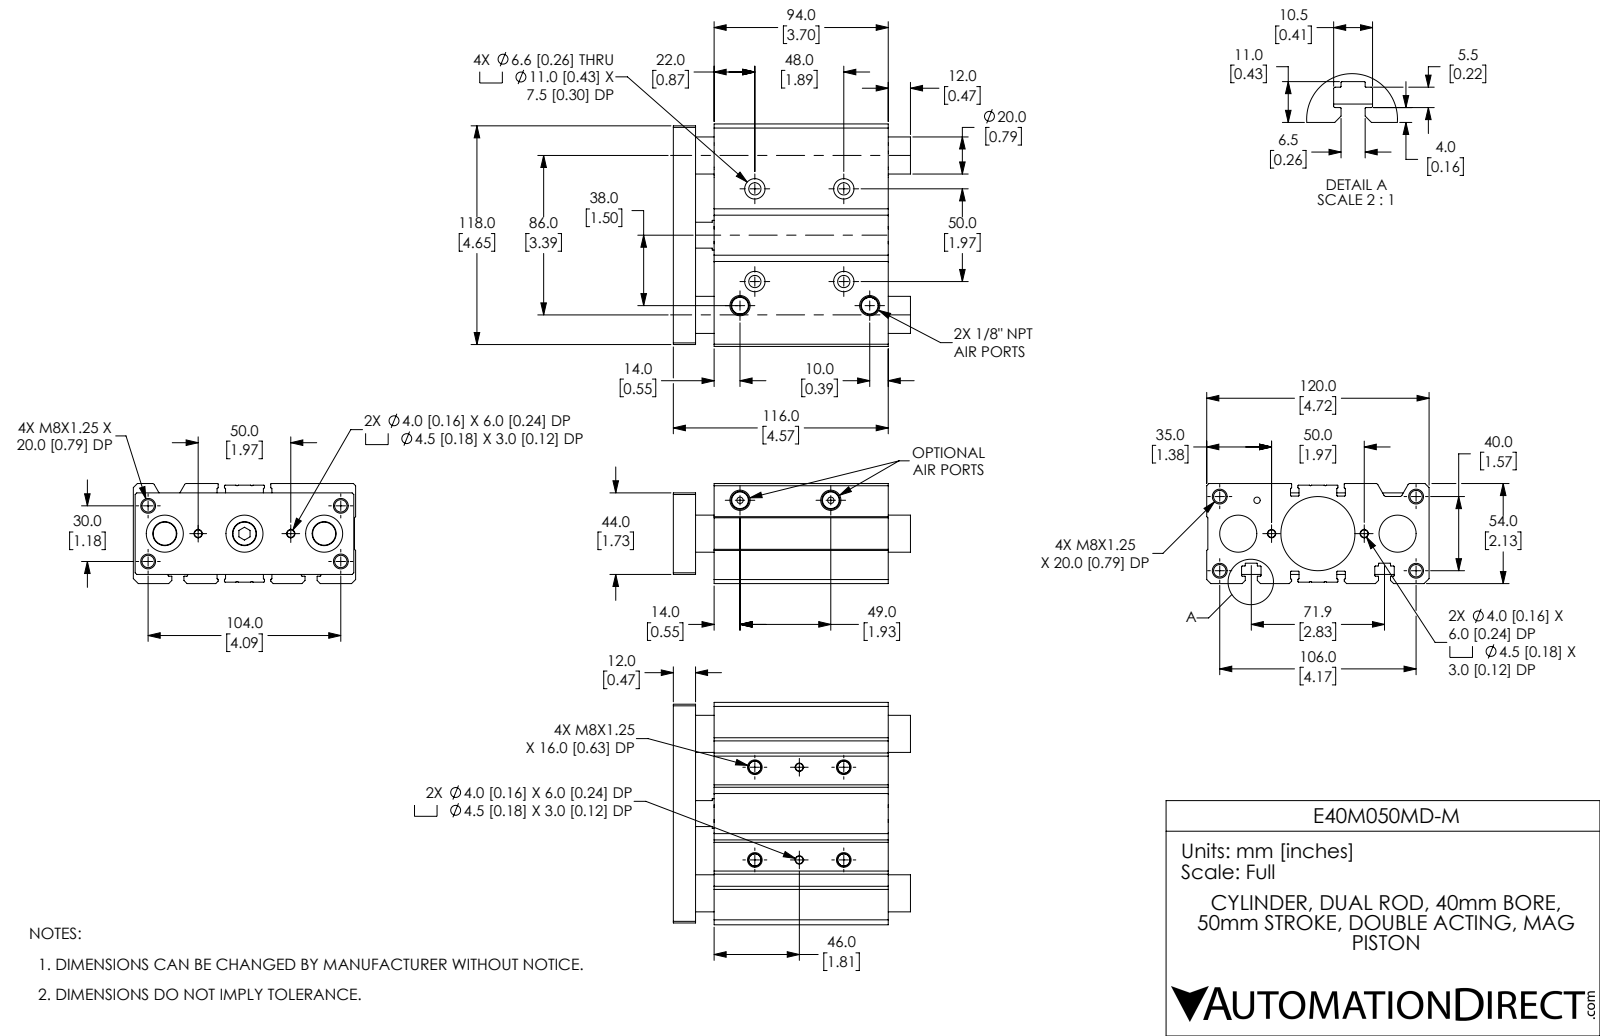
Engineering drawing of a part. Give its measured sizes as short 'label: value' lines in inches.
name: E40M050MD-M; E40M050MD-M_BODY; E40M050MD-M_ENDPLATE
written by: SolidWorks 2019 (CONFIG_CONTROL_DESIGN)
unit: in
bodies: 5 solids, 427 faces (139 planar, 194 cylindrical, 94 other)
size: 5.039 × 4.724 × 2.126
volume: 34.72 in³; area: 203.2 in²
holes: 12× ⌀0.262, 4× ⌀0.157, 4× ⌀0.177, 4× ⌀0.26, 4× ⌀0.433, 3× ⌀0.135, 3× ⌀0.394, 3× ⌀0.787, 2× ⌀0.43, 2× ⌀0.51, 1× ⌀0.787, 1× ⌀1.575
bosses: 1× ⌀0.63, 1× ⌀0.51
rounds: 32× R0.008, 28× R0.016, 4× R0.047, 2× R0.012
face distances: 2.126, 0.472, 4.567, 0.866, 0.394, 4.094, 3.701, 3.898, 4.724, 0.163
hole spacings: 0.201, 0.689, 0.88, 0.945, 1.216, 1.355, 1.378, 1.969
